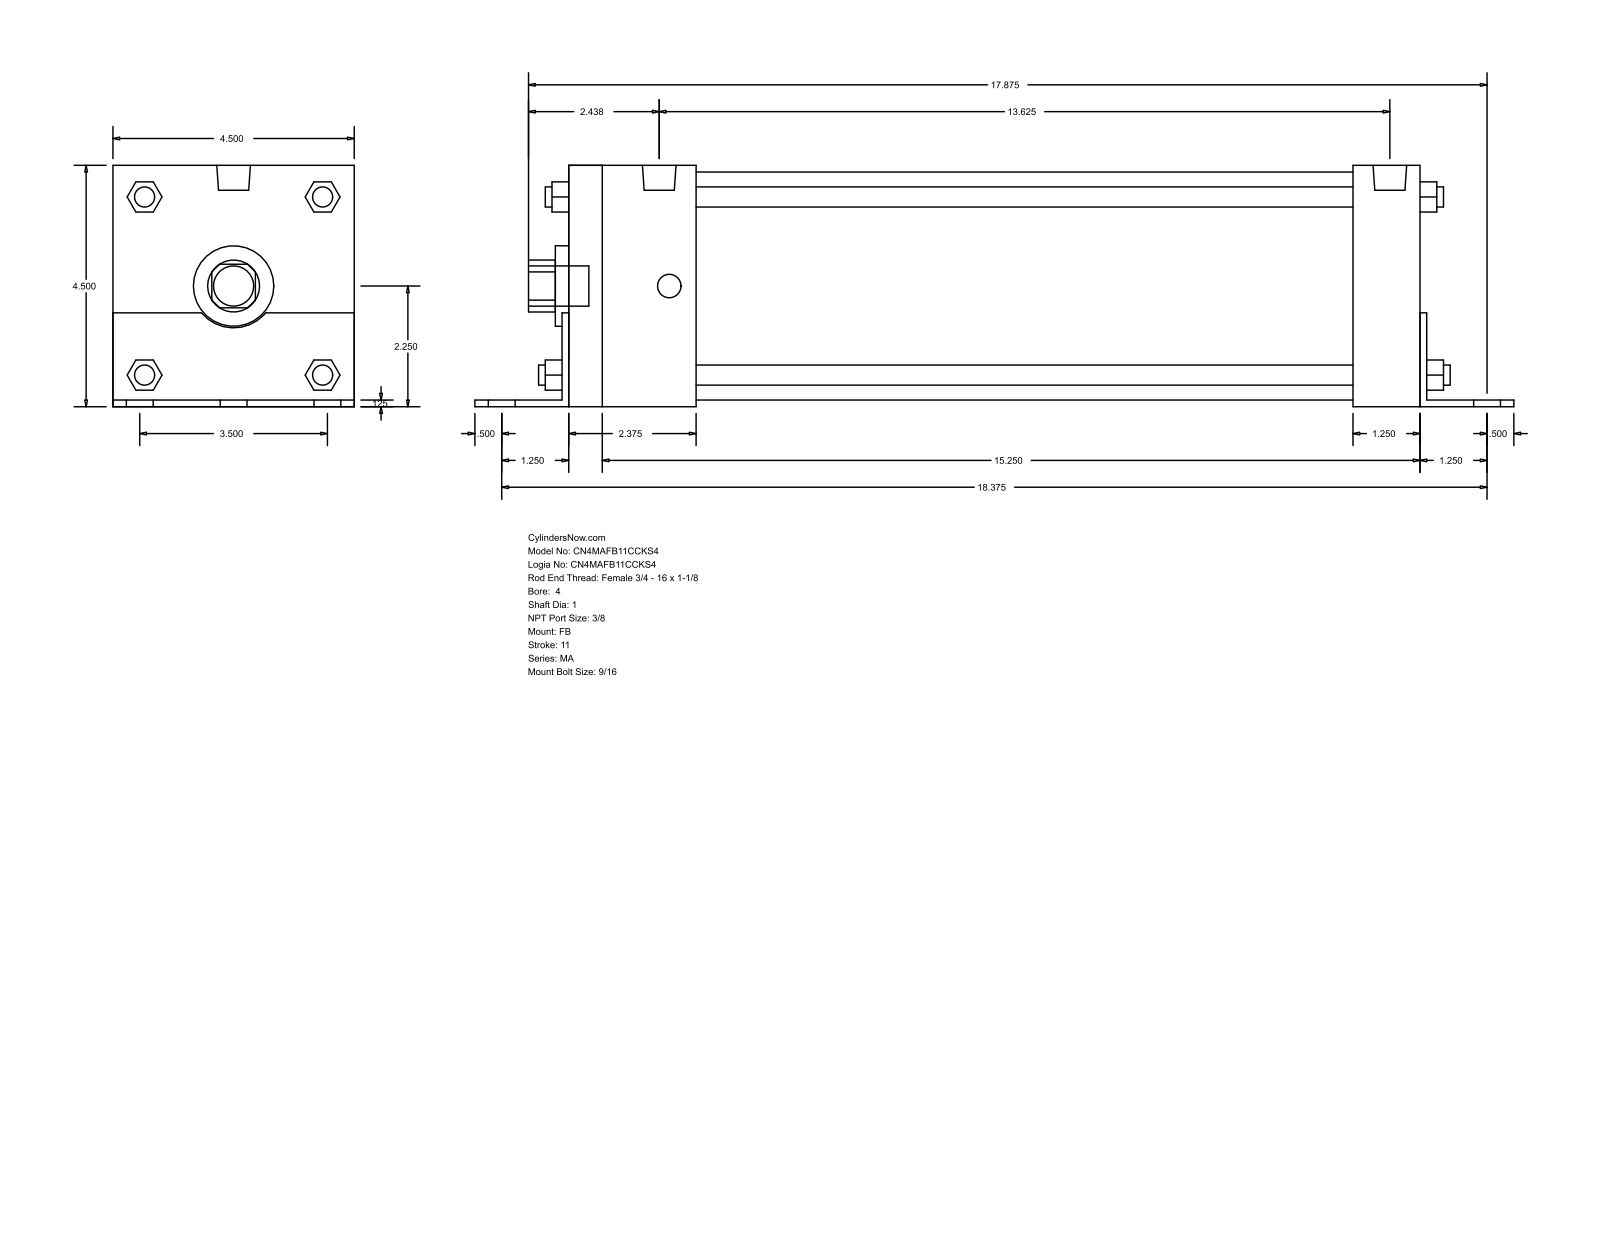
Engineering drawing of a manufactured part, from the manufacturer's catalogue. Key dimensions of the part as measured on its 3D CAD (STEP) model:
Part name (STEP PRODUCT): MA_FB__0400_1
STEP written by: GSSL Pune (CONFIG_CONTROL_DESIGN)
Units: millimetres
Bodies: 0 solids, 140 faces (105 planar, 35 cylindrical, 0 other)
Overall size (bounding box): 492.12 × 114.35 × 114.3
Round holes (diameter × count): ⌀25.4 ×1, ⌀38.1 ×1, ⌀107.95 ×1
Round bosses / shafts (diameter × count): ⌀14.29 ×6, ⌀11.11 ×4, ⌀9.53 ×4, ⌀15.93 ×2, ⌀19.05 ×1
Partial cylindrical surfaces — rounded edges, fillets, slot ends (radius × count): R12.29 ×1, R19.81 ×1
Main face-to-face distances: 114.3, 3.17, 114.35, 3.12, 111.18, 403.22, 3.18, 409.57, 406.4, 406.39
